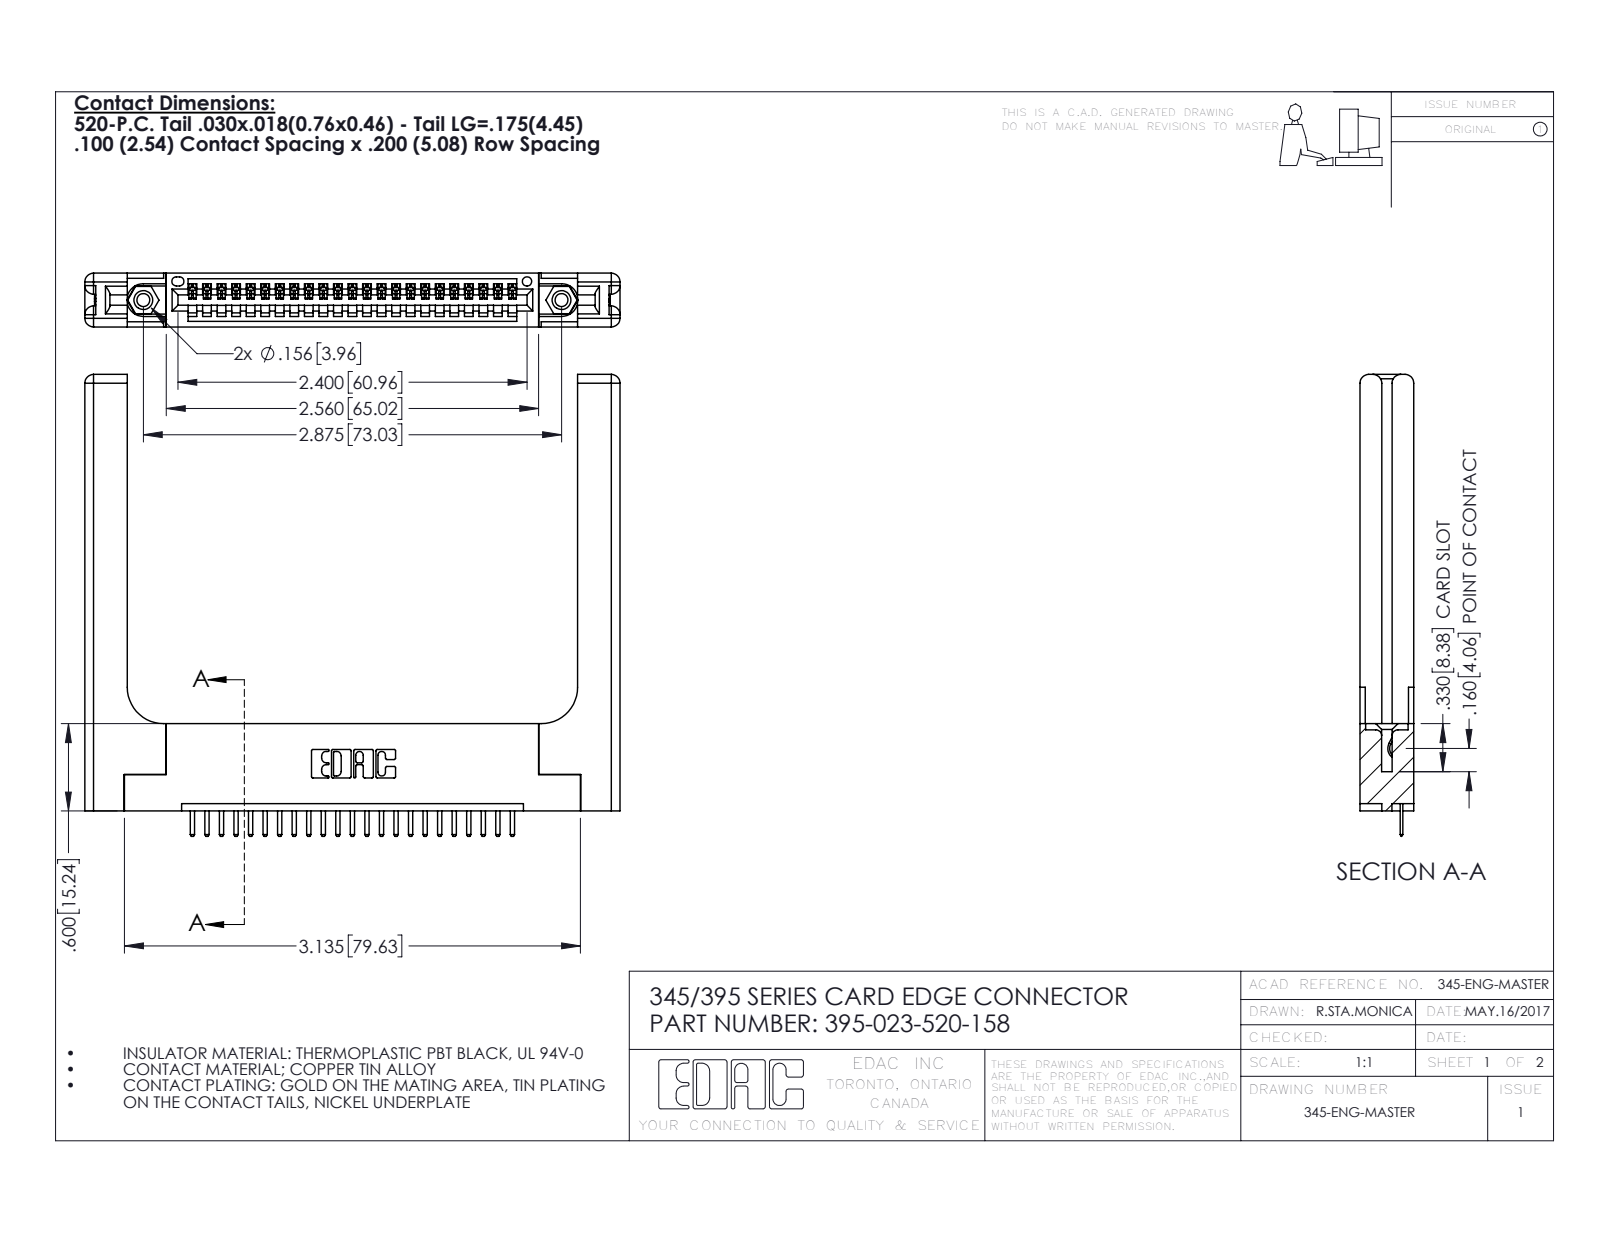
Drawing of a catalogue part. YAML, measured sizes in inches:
part_name: "395-023-520-158; 345-292-001_345-293-120; 345-220-058_345-220-058; 345-250-001_345-250-001-102 (+1 more)"
step_written_by: "SolidWorks 2016 (CONFIG_CONTROL_DESIGN)"
units: inches
bodies: {solids: 28, faces: 1808, planar: 1194, cylindrical: 554, other: 60}
overall_size: [3.679, 3.175, 0.37]
volume: 1.047
surface_area: 25.31
round_holes:
  - {diameter: 0.089, count: 2}
  - {diameter: 0.125, count: 2}
  - {diameter: 0.156, count: 2}
  - {diameter: 0.064, count: 1}
round_bosses_or_shafts:
  - {diameter: 0.155, count: 2}
partial_cylinders:
  - {radius: 0.01, count: 48}
  - {radius: 0.006, count: 46}
  - {radius: 0.01, count: 22}
  - {radius: 0.06, count: 16}
  - {radius: 0.007, count: 6}
  - {radius: 0.031, count: 6}
  - {radius: 0.026, count: 3}
  - {radius: 0.03, count: 2}
face_to_face_distances: [0.37, 0.072, 0.298, 0.15, 0.148, 0.2, 0.077, 0.22, 0.098, 0.272]
hole_center_spacings: [0.27, 2.641, 2.875]
